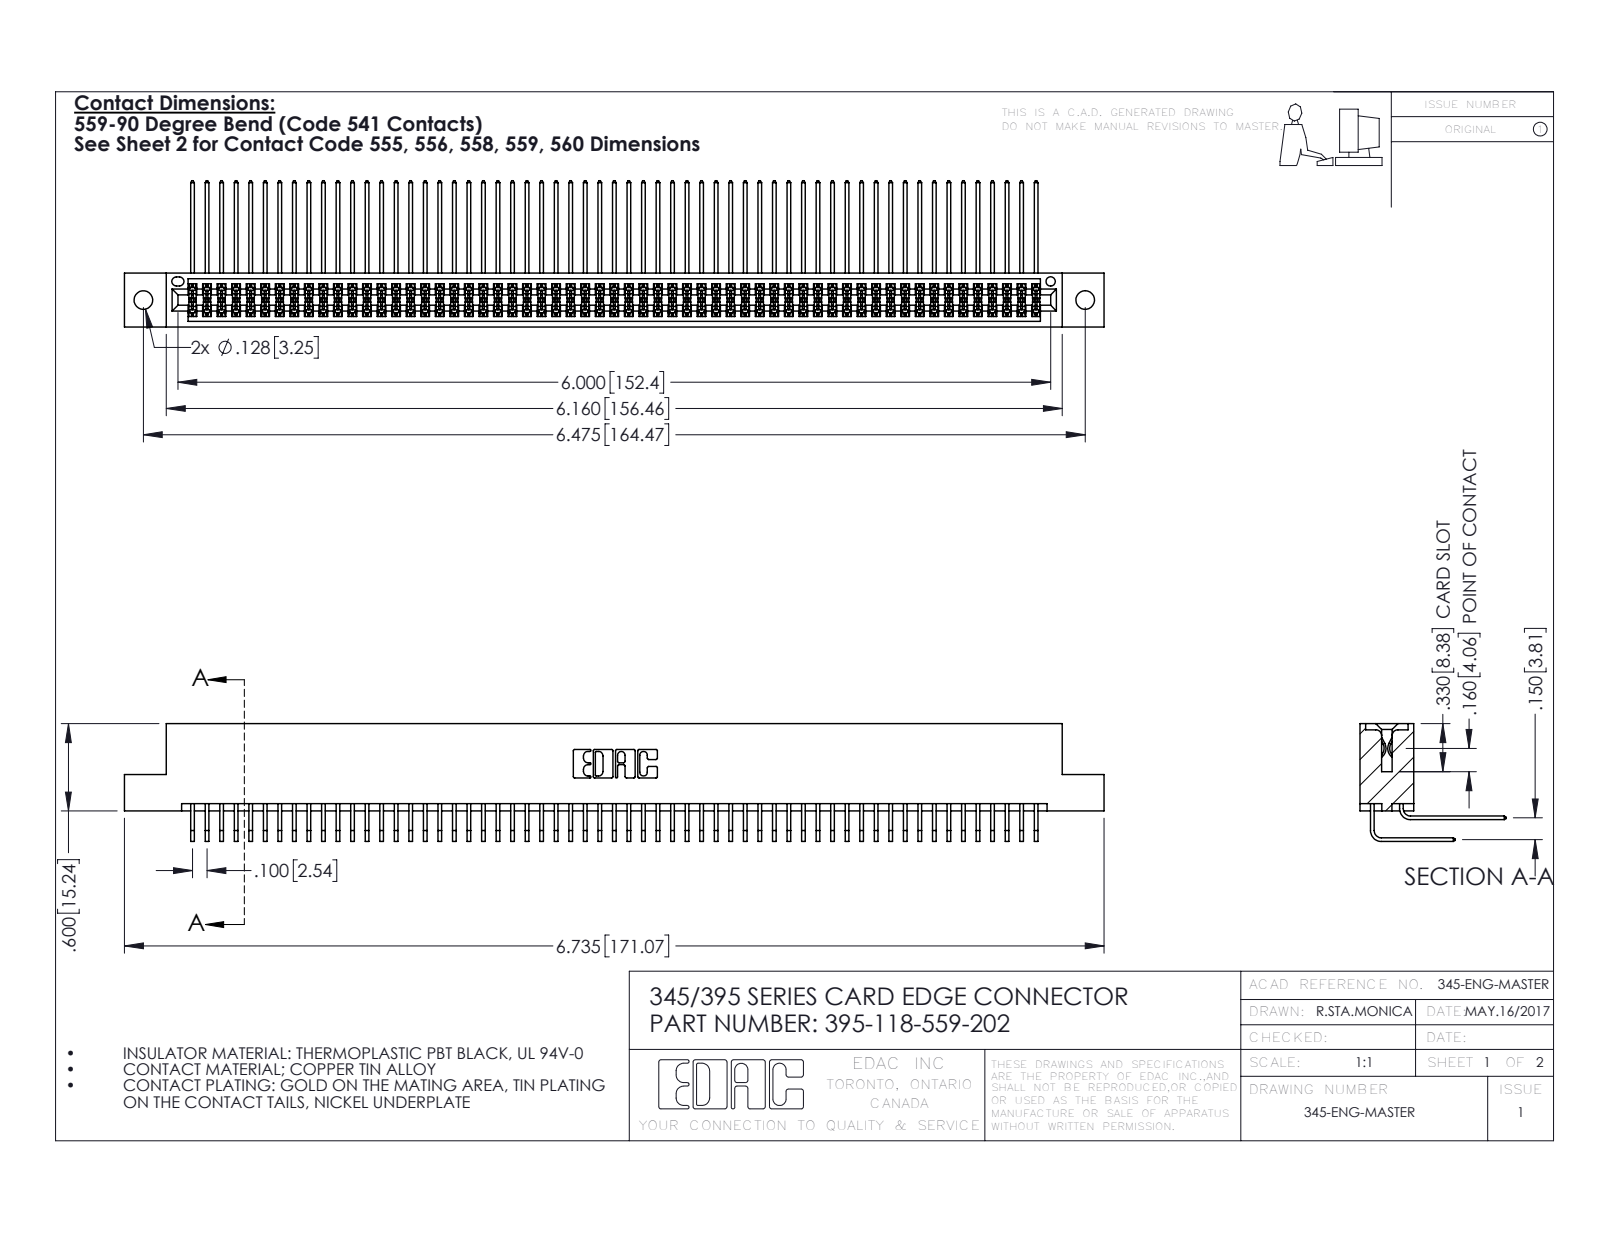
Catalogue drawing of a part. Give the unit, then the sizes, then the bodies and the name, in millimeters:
Units: millimetres
Overall size (bounding box): 171.1 × 25.5 × 20.5
Round holes (diameter × count): ⌀3.3 ×2, ⌀1.6 ×1
Partial cylindrical surfaces — rounded edges, fillets, slot ends (radius × count): R0.2 ×178, R0.3 ×22, R0.2 ×6, R0.8 ×6, R0.7 ×3, R0.4 ×2, R0.5 ×2, R0.6 ×2
Main face-to-face distances: 1.8, 7.6, 5.1, 9.4, 2.5, 6.9, 0.6, 5.7, 4.4, 3.8
Hole centre spacings: 6.9, 158.5, 164.5
Volume: 17 420 mm³ · Surface area: 29 010 mm²
Bodies: 119 solids, 6262 faces (4210 planar, 2052 cylindrical, 0 other)
Part name (STEP PRODUCT): 345-292-001_559 Tail - 2; 345-292-001_558 559 Tail - 1; 395-118-559-202; 345 Part_Flush Mounting Lugs - 0.128 Dia
STEP written by: SolidWorks 2016 (CONFIG_CONTROL_DESIGN)
